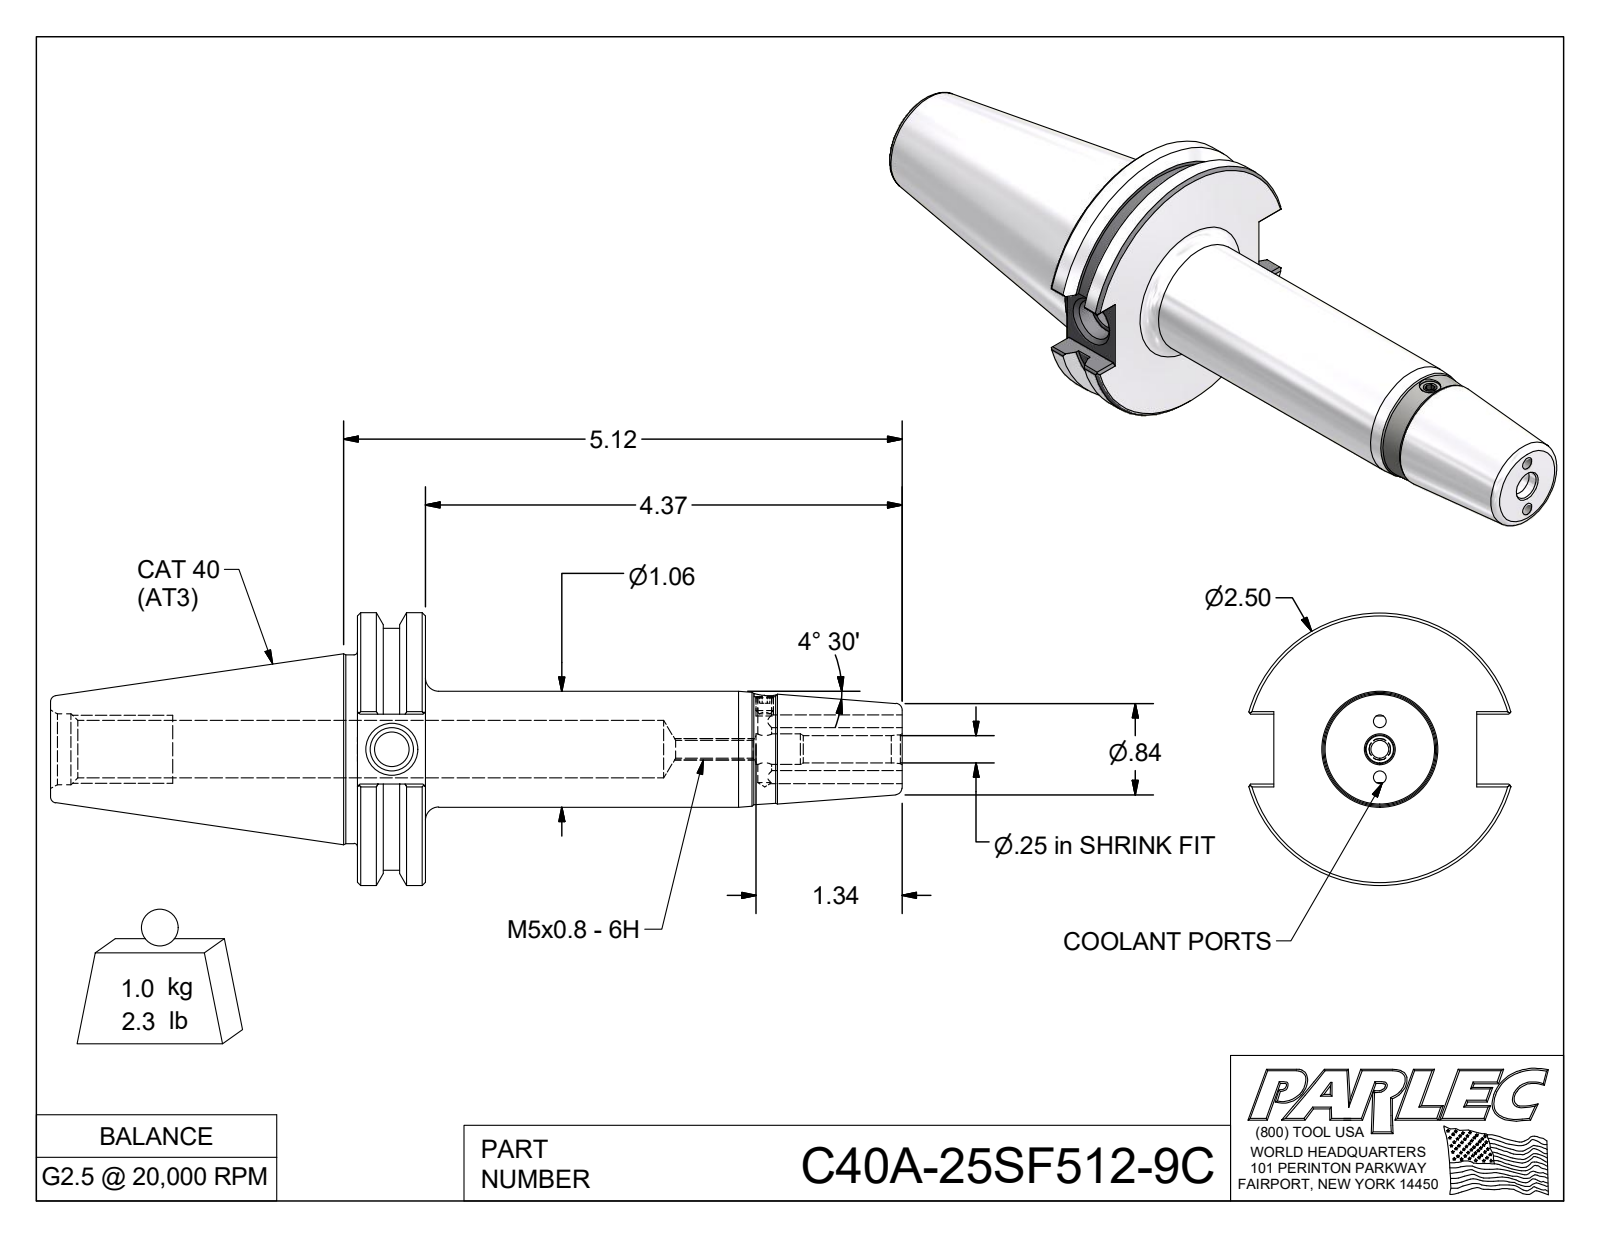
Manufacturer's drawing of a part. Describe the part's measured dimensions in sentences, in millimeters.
The part is named "C40A-25SF512-9C; 029-060". Its 3-D file was written by "Autodesk Inventor 2018 (AUTOMOTIVE_DESIGN)". It is 2 solids with 94 faces: 41 planar, 21 cylindrical and 32 other. Overall it measures 198.3 by 63.5 by 61 millimeters. Its volume is 149 500 cubic millimeters and its surface area 33 200 square millimeters. Round holes: 2 of diameter 3, 1 of diameter 3.3, 1 of diameter 4.1, 1 of diameter 5, 1 of diameter 6.4, 1 of diameter 7.1, 1 of diameter 8, 1 of diameter 10.1, 1 of diameter 13.4, 1 of diameter 16.5. Round bosses or shafts: 1 of diameter 63.5, 1 of diameter 56.4, 1 of diameter 43.9, 1 of diameter 27, 1 of diameter 4. The main face-to-face distances are 15.9, 126.8, 110.9, 16.3, 47.2, 71.4, 87.3, 198.3, 81.3, 9.9. The hole center spacings are 6.5, 13.
